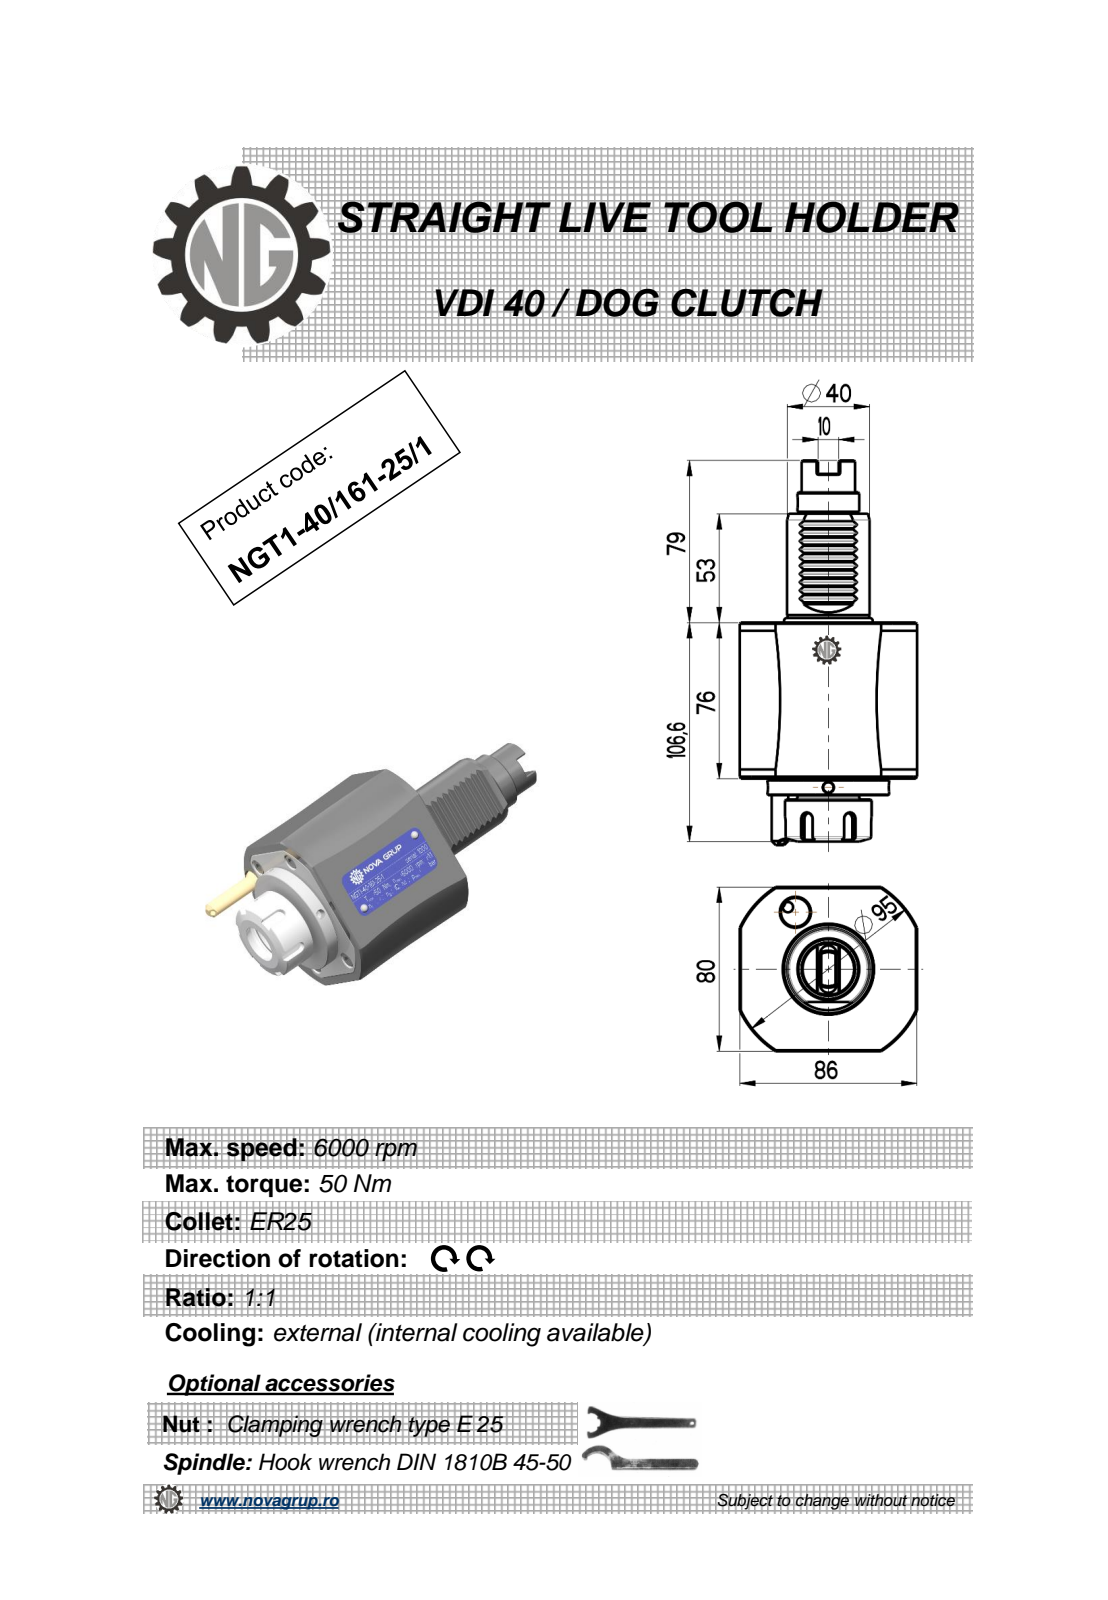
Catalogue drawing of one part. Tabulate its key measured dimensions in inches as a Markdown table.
| quantity | value |
| --- | --- |
| part name | NGT1_40_161_25_1 |
| STEP written by | PRO/ENGINEER BY PARAMETRIC TECHNOLOGY CORPORATION, 2010280 (CONFIG_CONTROL_DESIGN) |
| units | inches |
| bodies | 1 solid, 299 faces (111 planar, 73 cylindrical, 115 other) |
| overall size | 7.376 × 3.386 × 3.15 |
| volume | 36.61 in³ |
| surface area | 83.41 in² |
| round holes (diameter × count) | 0.197 × 3, 0.118 × 1, 0.165 × 1 |
| round bosses / shafts (diameter × count) | 2.323 × 1, 1.89 × 1, 1.654 × 1, 1.575 × 1, 1.299 × 1, 1.181 × 1, 1.024 × 1, 0.315 × 1 |
| partial cylindrical surfaces (radius × count) | 0.012 × 10, 0.009 × 6, 0.01 × 6, 0.118 × 5, 0.02 × 2, 0.492 × 1, 1.87 × 1 |
| main face-to-face distances | 2.992, 3.15, 3.386, 3.307, 0.315, 0.02, 0.111, 3.012, 0.295, 5.098 |
| hole center spacings | 5.463 |
